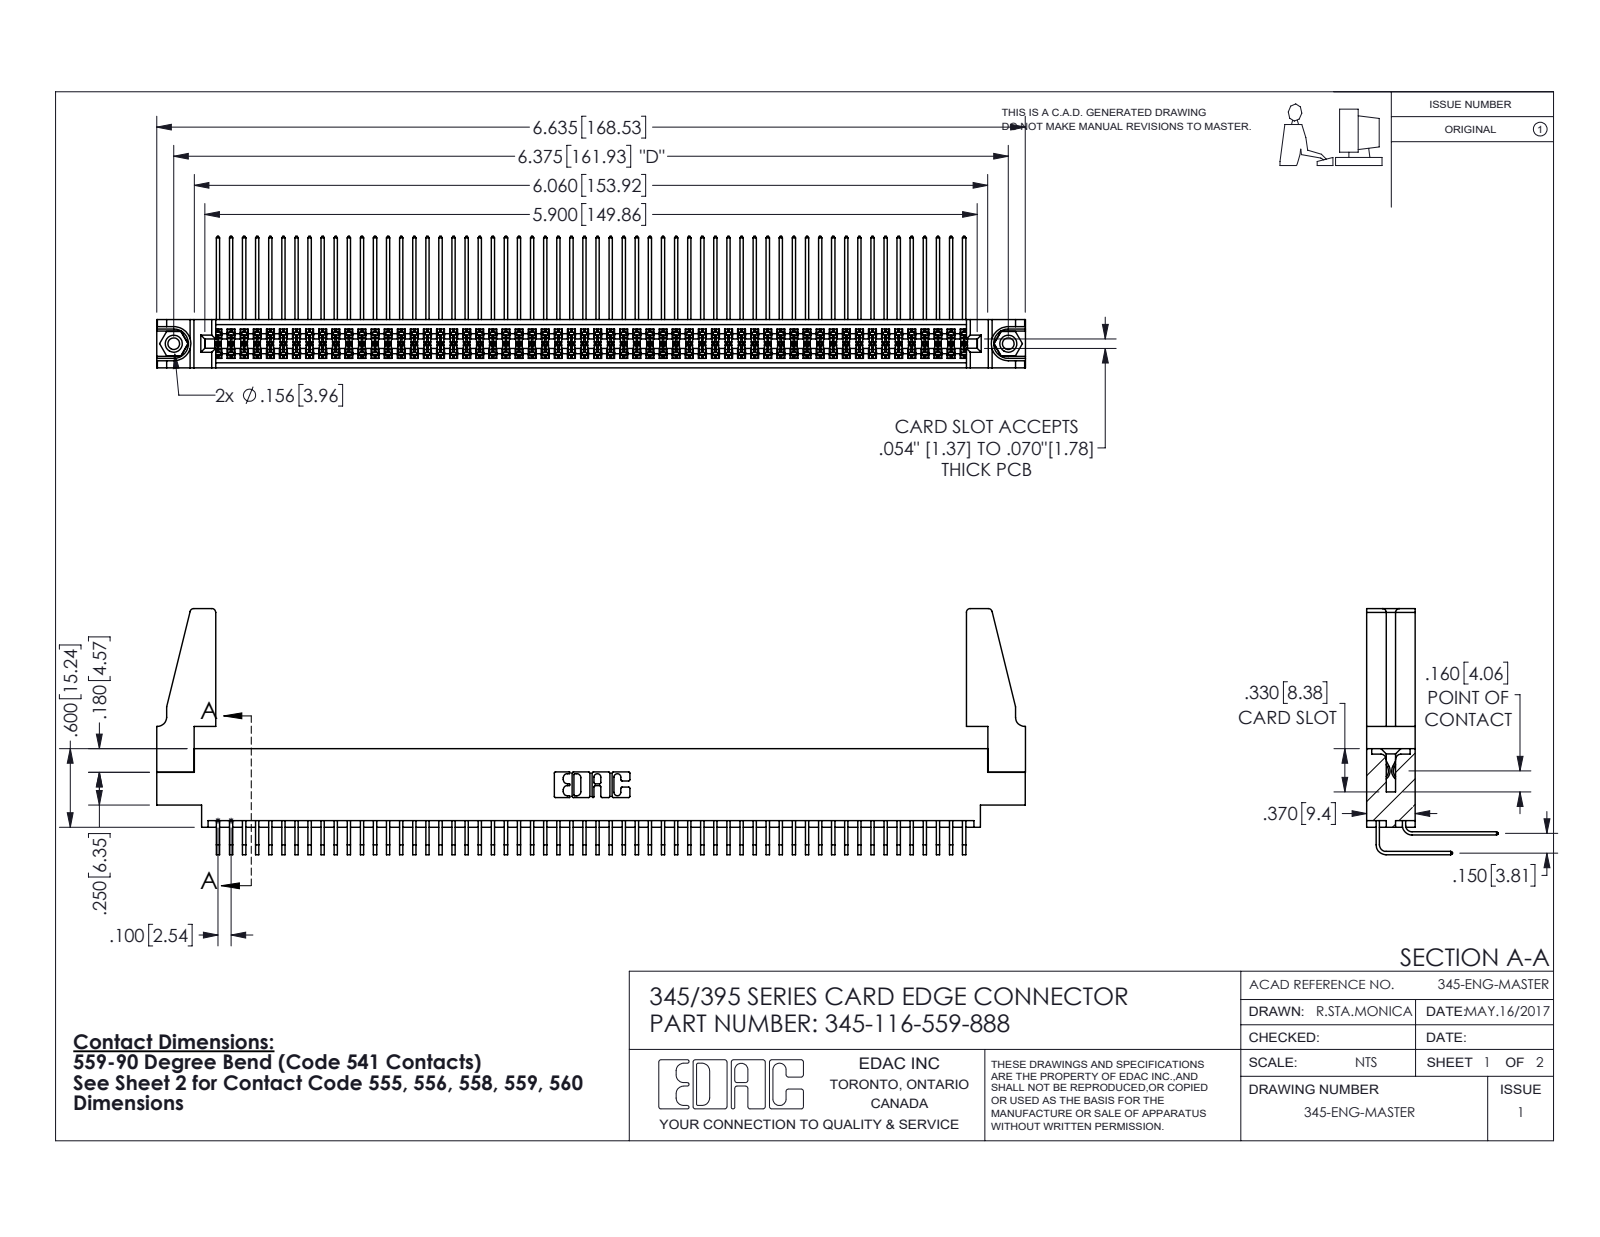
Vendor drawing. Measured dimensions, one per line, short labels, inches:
name: 345-250-001_345-250-001-102; 345-292-001_558 559 Tail - 1; 345-292-001_559 Tail - 2; 345 Part_0.170 Offset - 0.156 Dia-TH (+2 more)
written by: SolidWorks 2016 (CONFIG_CONTROL_DESIGN)
unit: in
bodies: 121 solids, 6286 faces (4216 planar, 2054 cylindrical, 16 other)
size: 6.636 × 1.879 × 1.005
volume: 1.241 in³; area: 49.55 in²
holes: 2× ⌀0.089, 2× ⌀0.125, 2× ⌀0.156, 1× ⌀0.064
bosses: 2× ⌀0.155
rounds: 231× R0.006, 22× R0.01, 8× R0.03, 6× R0.007, 6× R0.031, 3× R0.026, 2× R0.014, 2× R0.019
face distances: 0.072, 0.298, 0.37, 0.2, 0.098, 0.272, 0.025, 0.225, 0.15, 0.175
hole spacings: 0.27, 6.139, 6.375
